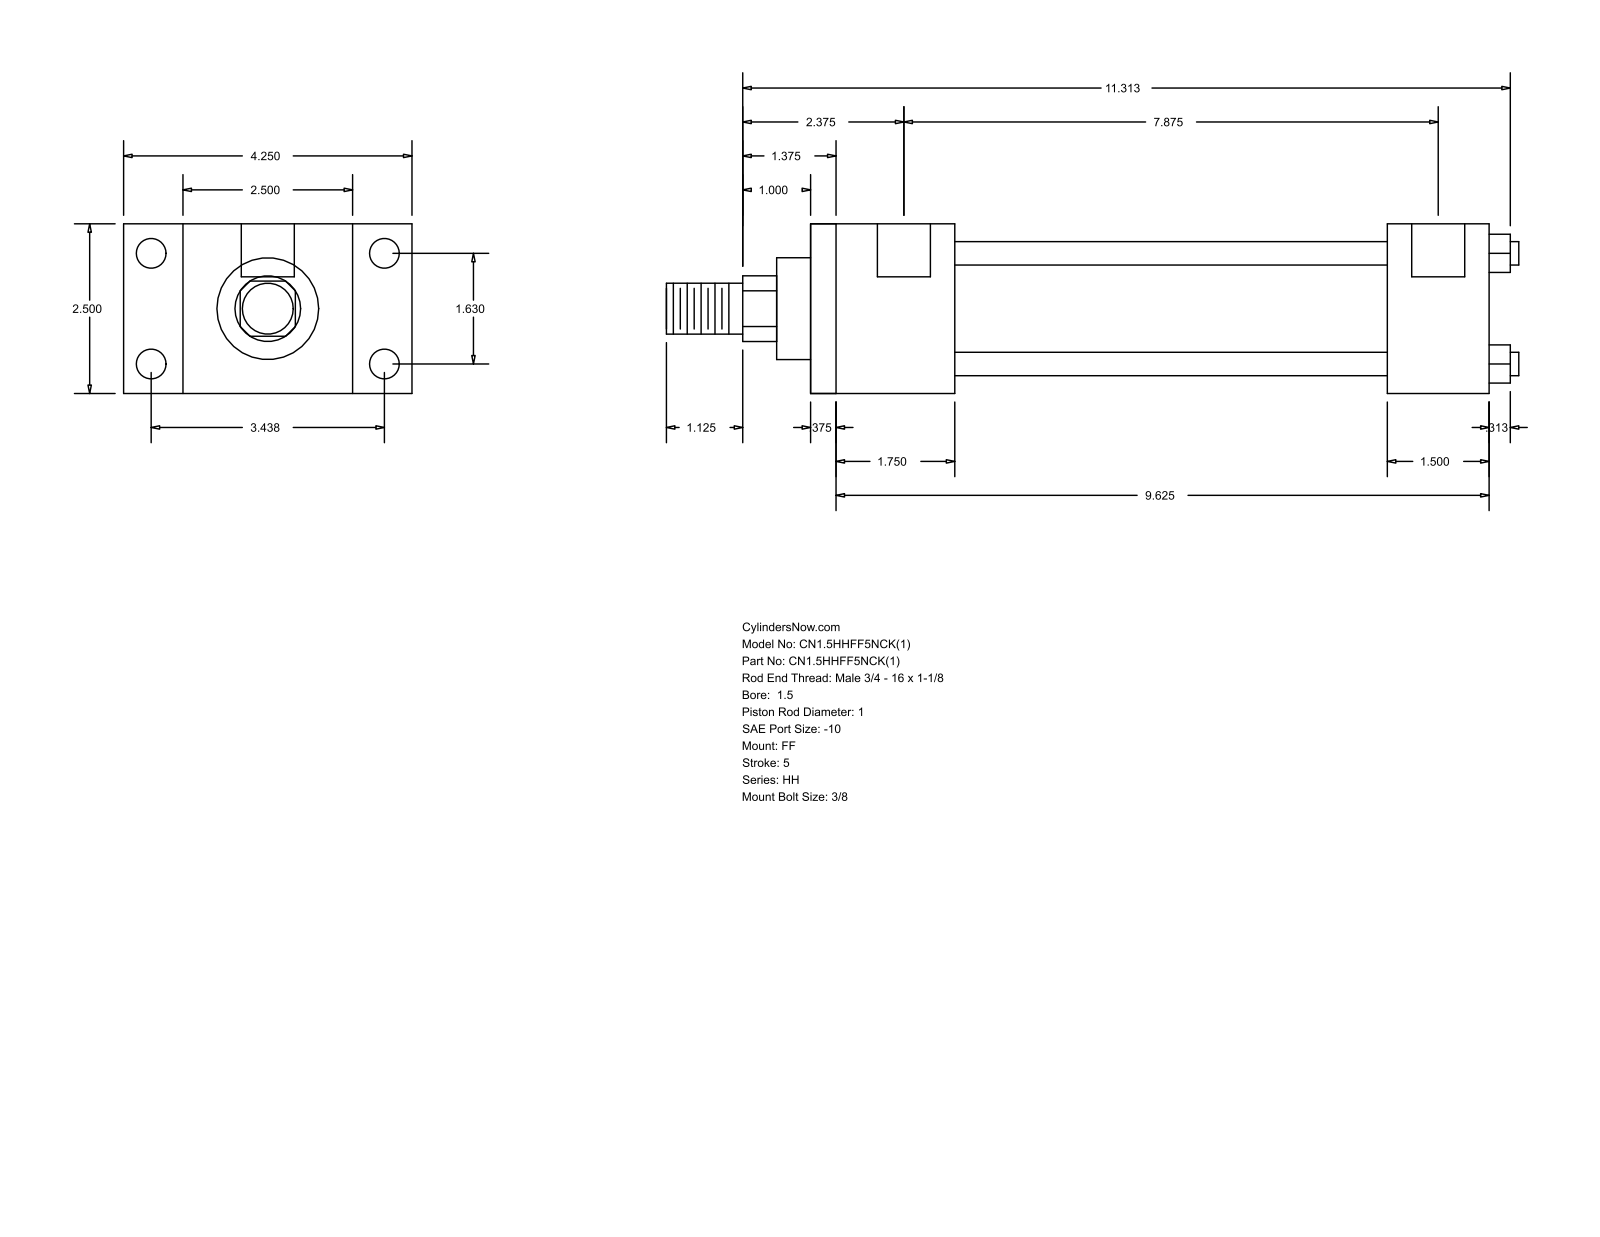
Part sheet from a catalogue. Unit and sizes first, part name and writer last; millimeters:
Units: millimetres
Overall size (bounding box): 319.09 × 107.95 × 63.5
Round holes (diameter × count): ⌀5.56 ×4, ⌀11.13 ×4, ⌀19.84 ×2
Round bosses / shafts (diameter × count): ⌀8.76 ×4, ⌀44.45 ×1, ⌀38.1 ×1, ⌀25.4 ×1, ⌀19.05 ×1
Partial cylindrical surfaces — rounded edges, fillets, slot ends (radius × count): R12.29 ×1
Main face-to-face distances: 63.5, 254, 9.52, 244.48, 38.1, 53.98, 44.46, 200.02, 215.9, 206.38
Hole centre spacings: 1.59, 41.4, 87.32, 96.64, 201.61, 203.2, 200.02
Bodies: 0 solids, 92 faces (64 planar, 28 cylindrical, 0 other)
Part name (STEP PRODUCT): HH_FF__0150_1
STEP written by: GSSL Pune (CONFIG_CONTROL_DESIGN)
